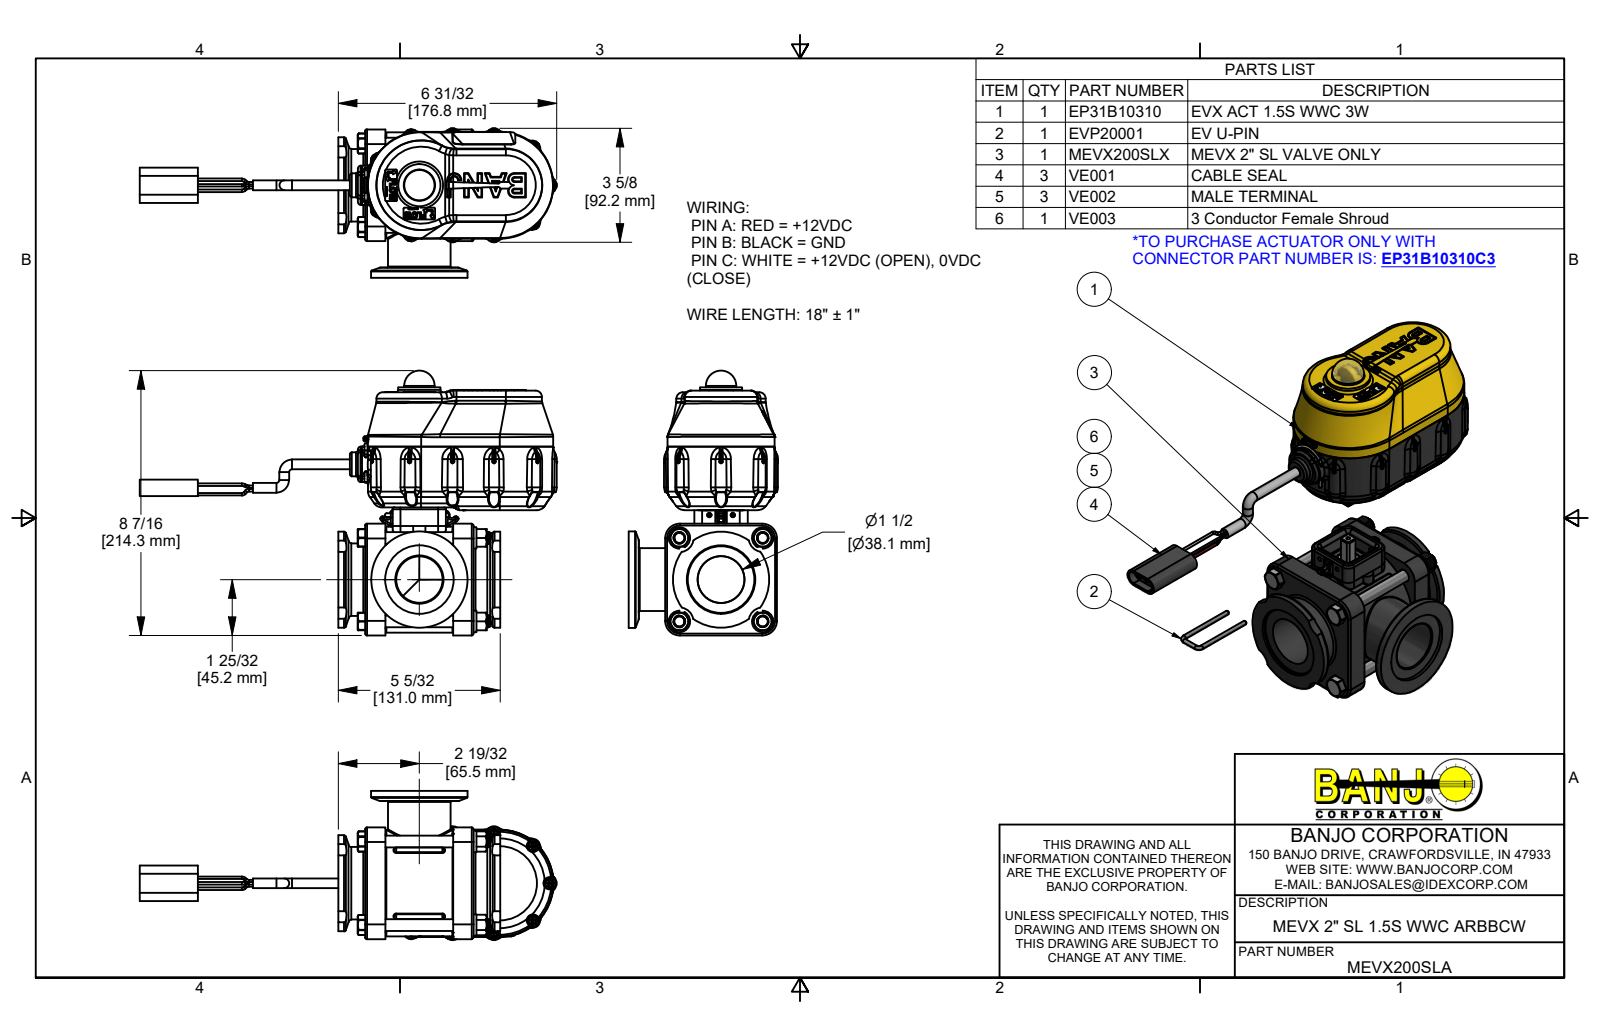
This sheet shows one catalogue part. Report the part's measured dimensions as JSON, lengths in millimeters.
{"part_name": "MEVX200SLA; EP31B10310; B61905PPHS; B632038PM (+8 more)", "step_written_by": "Autodesk Inventor 2019 (AUTOMOTIVE_DESIGN)", "units": "millimeters", "bodies": {"solids": 105, "faces": 11753, "planar": 3228, "cylindrical": 3385, "other": 5140}, "overall_size": [337.6, 214.3, 120.9], "volume_mm3": 1144000, "surface_area_mm2": 442600, "round_holes": [[2.4, 11], [3.8, 11], [2, 7], [3.8, 7], [2.7, 4], [3.2, 4], [3.5, 4], [3.8, 4], [4.3, 4], [6.4, 4], [7.8, 4], [9.8, 4]], "round_bosses_or_shafts": [[8.2, 60], [2, 18], [6.4, 17], [3.6, 11], [2.7, 11], [2.2, 11], [1.5, 6], [9.5, 5]], "partial_cylinders_radius": [[0.3, 180], [1, 145], [0.3, 84], [0.5, 78], [0.1, 53], [1.5, 36], [0.8, 30], [2, 28]], "face_to_face_distances": [2.5, 42.8, 65.2, 1.5, 16.8, 71.6, 21.2, 67.1, 4.4, 50.4], "hole_center_spacings": [47.8, 67.5, 45.1, 68.3, 69.3, 96.2, 7.6, 12.4]}
